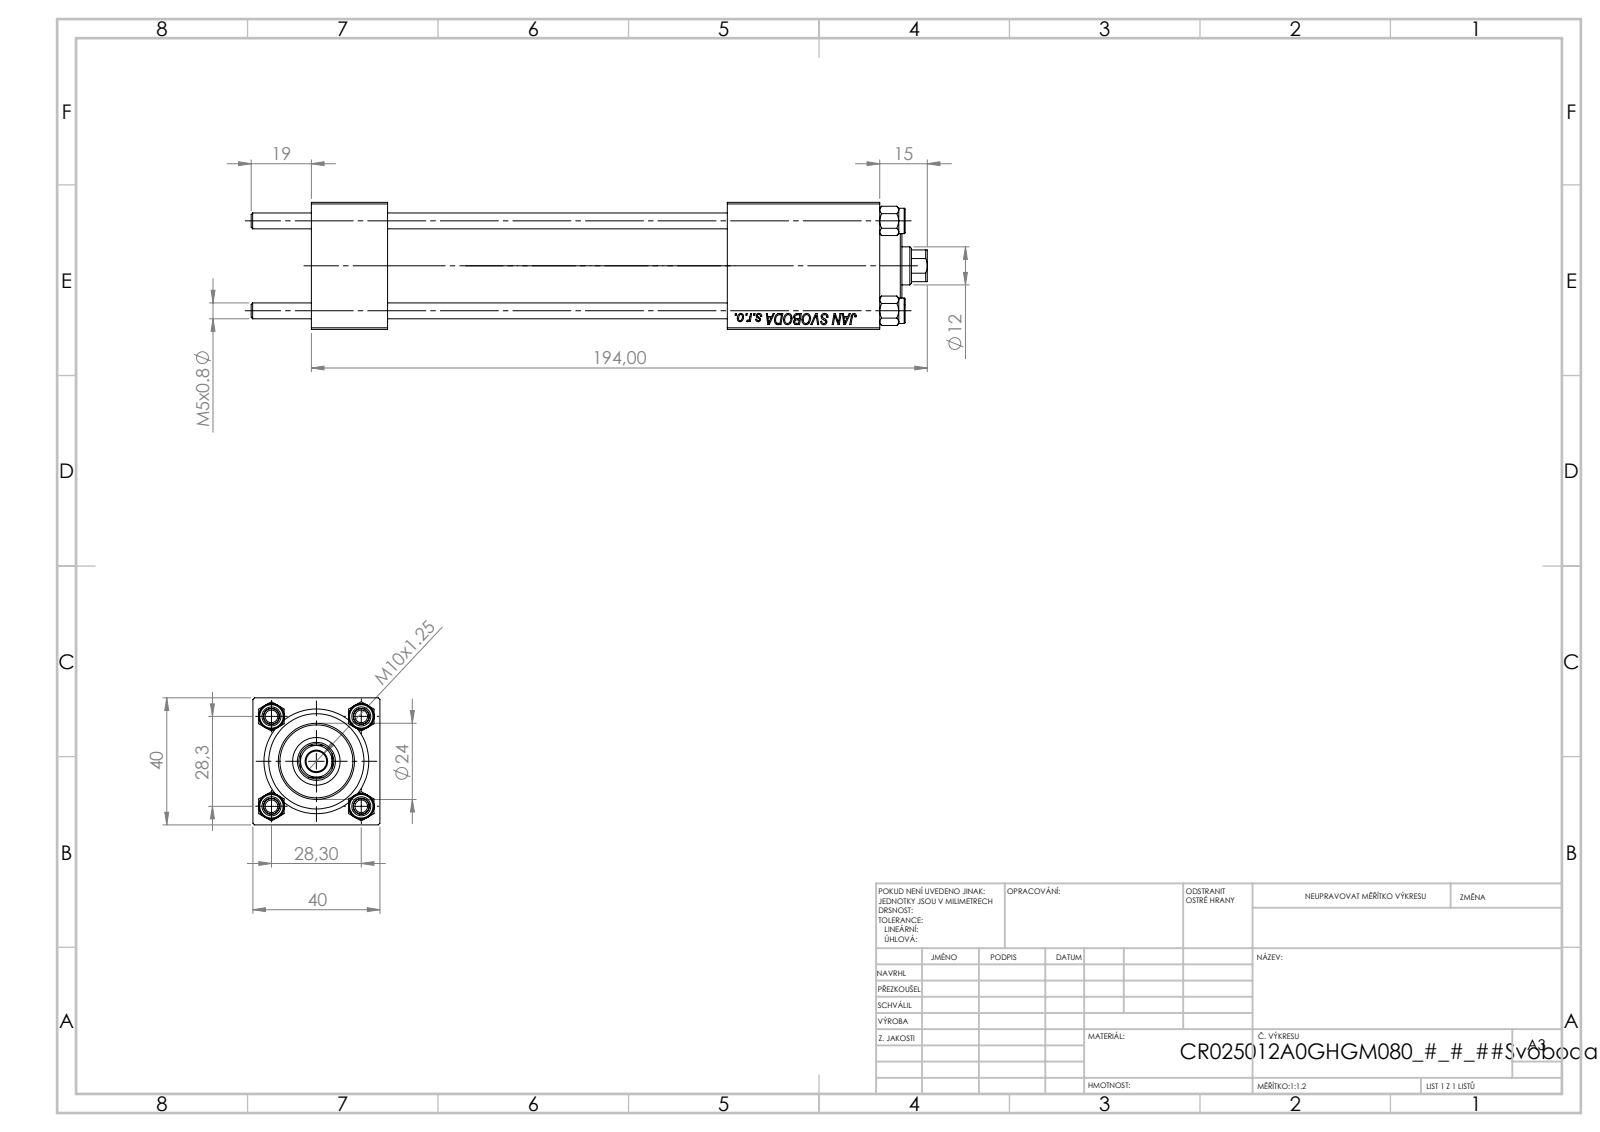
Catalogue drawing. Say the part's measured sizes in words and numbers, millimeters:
The part is named "V215CR_BODY_A; CR025_012_A_0_G_A_G_M_020_+#_##_TYCINKA; V215_VC_A; V215CR_VCP (+1 more)". Its 3-D file was written by "SolidWorks 2019 (CONFIG_CONTROL_DESIGN)". It is 11 solids with 1131 faces: 517 planar, 78 cylindrical and 536 other. Overall it measures 213 by 40 by 40 millimeters. Its volume is 172 156 cubic millimeters and its surface area 75 459 square millimeters. Round holes: 4 of diameter 5, 3 of diameter 20, 2 of diameter 7, 2 of diameter 13.16, 1 of diameter 6.5, 1 of diameter 12, 1 of diameter 15, 1 of diameter 25, 1 of diameter 30. Round bosses or shafts: 4 of diameter 8, 1 of diameter 31, 1 of diameter 24. Partial cylindrical surfaces (rounded edges, fillets, slot ends): 1 of radius 5.5. The main face-to-face distances are 40, 24, 179, 155, 150.3, 126.3, 28.7, 131, 107, 19.3. The hole center spacings are 20.01, 28.3, 40.02, 132.
